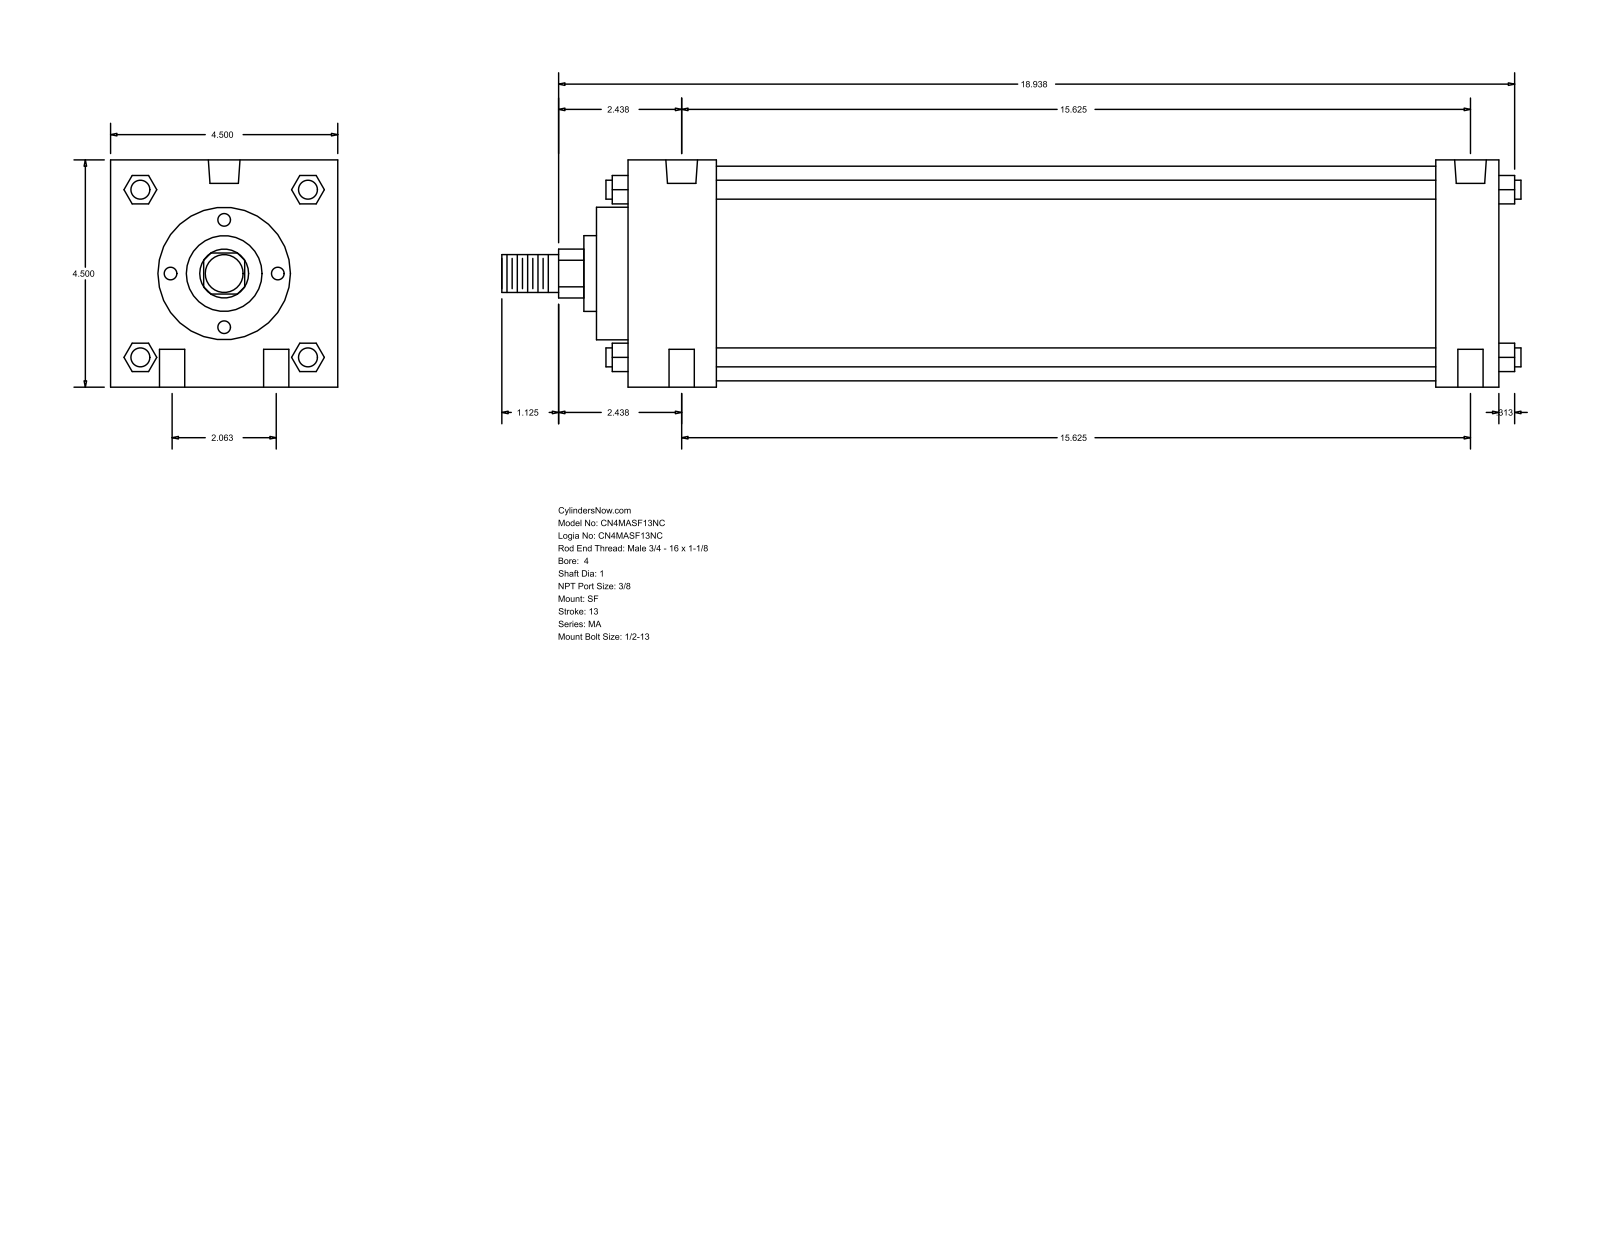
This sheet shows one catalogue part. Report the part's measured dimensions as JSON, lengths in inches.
{"part_name": "MA_SF__0400_1", "step_written_by": "GSSL Pune (CONFIG_CONTROL_DESIGN)", "units": "inches", "bodies": {"solids": 0, "faces": 126, "planar": 95, "cylindrical": 31, "other": 0}, "overall_size": [20.187, 4.5, 4.5], "round_holes": [[0.5, 4], [0.437, 2], [0.627, 2]], "round_bosses_or_shafts": [[0.375, 4], [4.25, 1], [2.625, 1], [1.5, 1], [1, 1], [0.75, 1]], "partial_cylinders_radius": [[0.484, 1]], "face_to_face_distances": [4.5, 17.25, 16, 1.25, 1.75, 14.25, 15.5, 17.875, 0.625, 2.375], "hole_center_spacings": [1.031, 15.659, 15.625, 2.062, 15.761, 15.25]}
